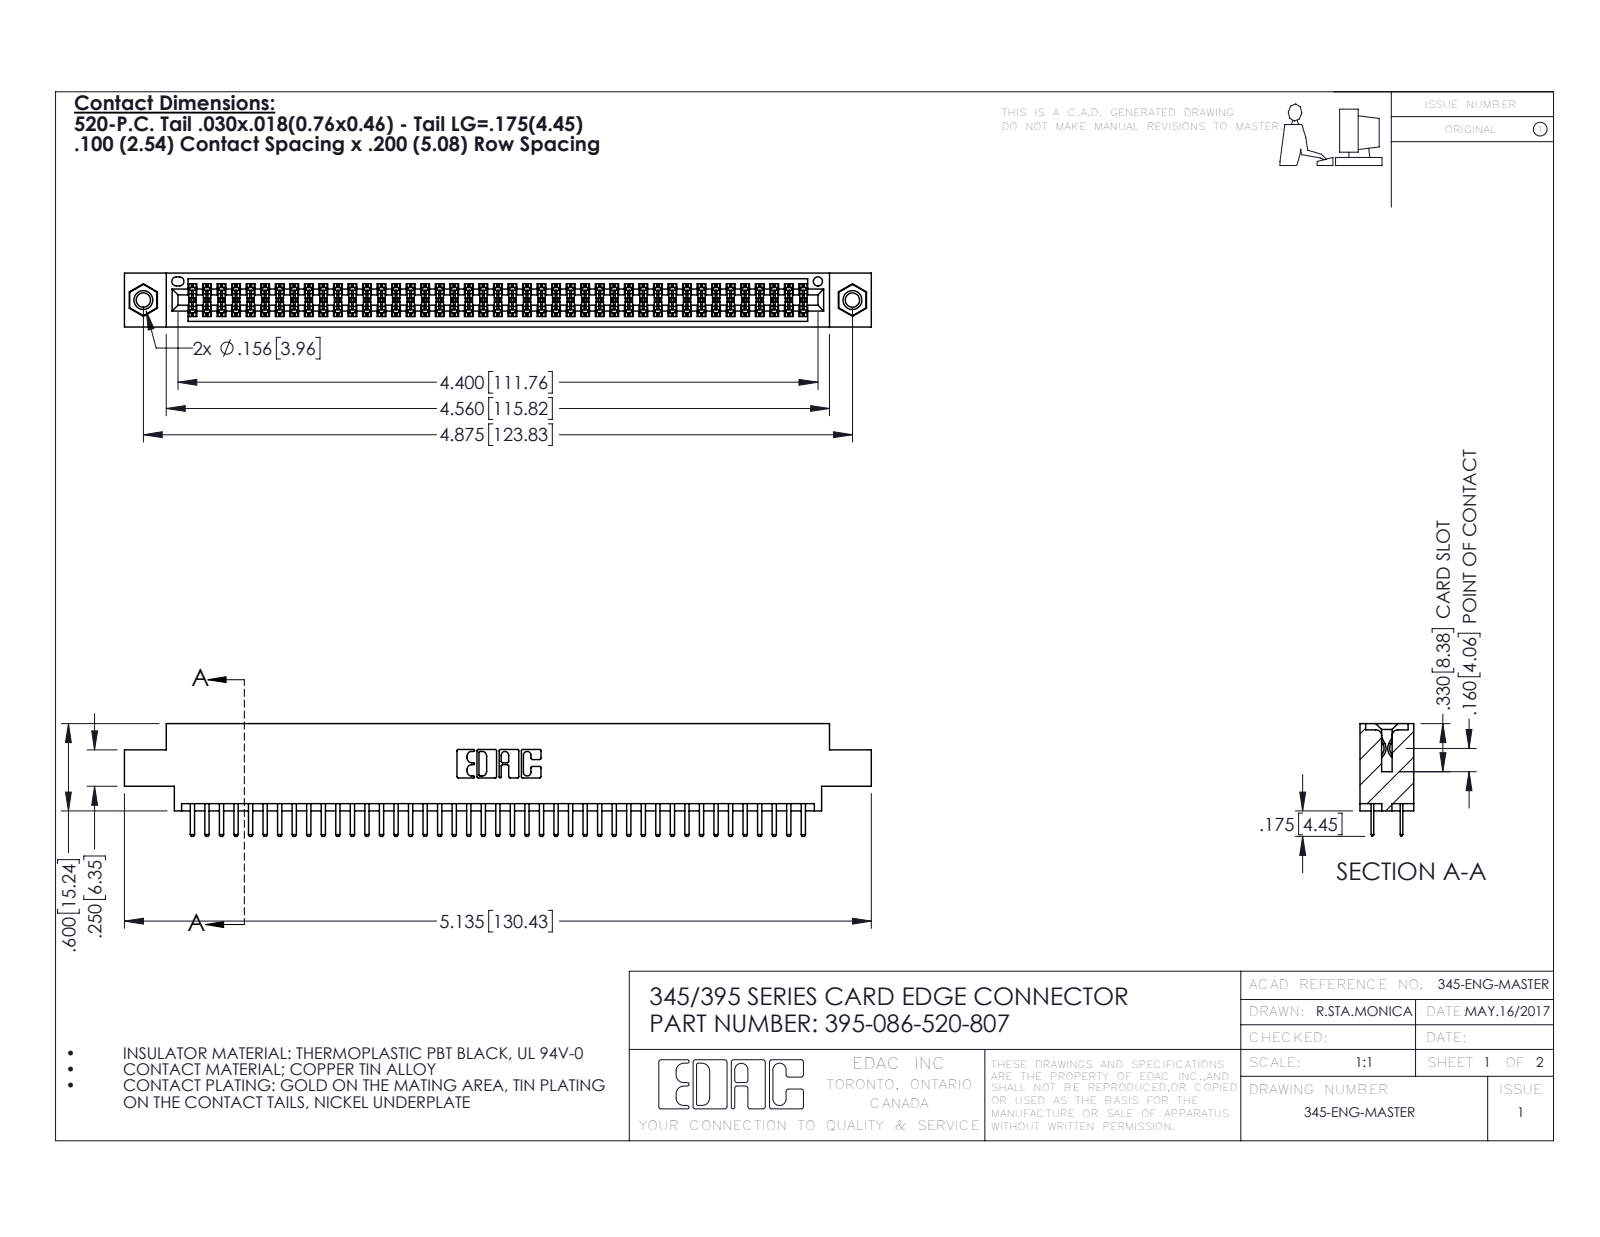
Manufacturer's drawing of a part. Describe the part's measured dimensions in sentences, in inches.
The part is named "345 Part_0.170 Offset - 0.156 Dia-TI; 395-086-520-807; 345-250-001_345-250-005-103; 345-292-001_345-293-120". Its 3-D file was written by "SolidWorks 2016 (CONFIG_CONTROL_DESIGN)". It is 89 solids with 4834 faces: 3126 planar, 1692 cylindrical and 16 other. Overall it measures 5.135 by 0.775 by 0.37 inches. Its volume is 0.764 cubic inches and its surface area 28.84 square inches. Round holes: 2 of diameter 0.098, 2 of diameter 0.125, 2 of diameter 0.156, 1 of diameter 0.064. Round bosses or shafts: 2 of diameter 0.155. Partial cylindrical surfaces (rounded edges, fillets, slot ends): 129 of radius 0.006, 90 of radius 0.01, 22 of radius 0.01, 6 of radius 0.007, 6 of radius 0.031, 3 of radius 0.026, 2 of radius 0.014, 2 of radius 0.019. The main face-to-face distances are 0.072, 0.298, 0.2, 0.37, 0.098, 0.272, 0.025, 0.225, 0.022, 0.175. The hole center spacings are 0.27, 4.639, 4.875.
